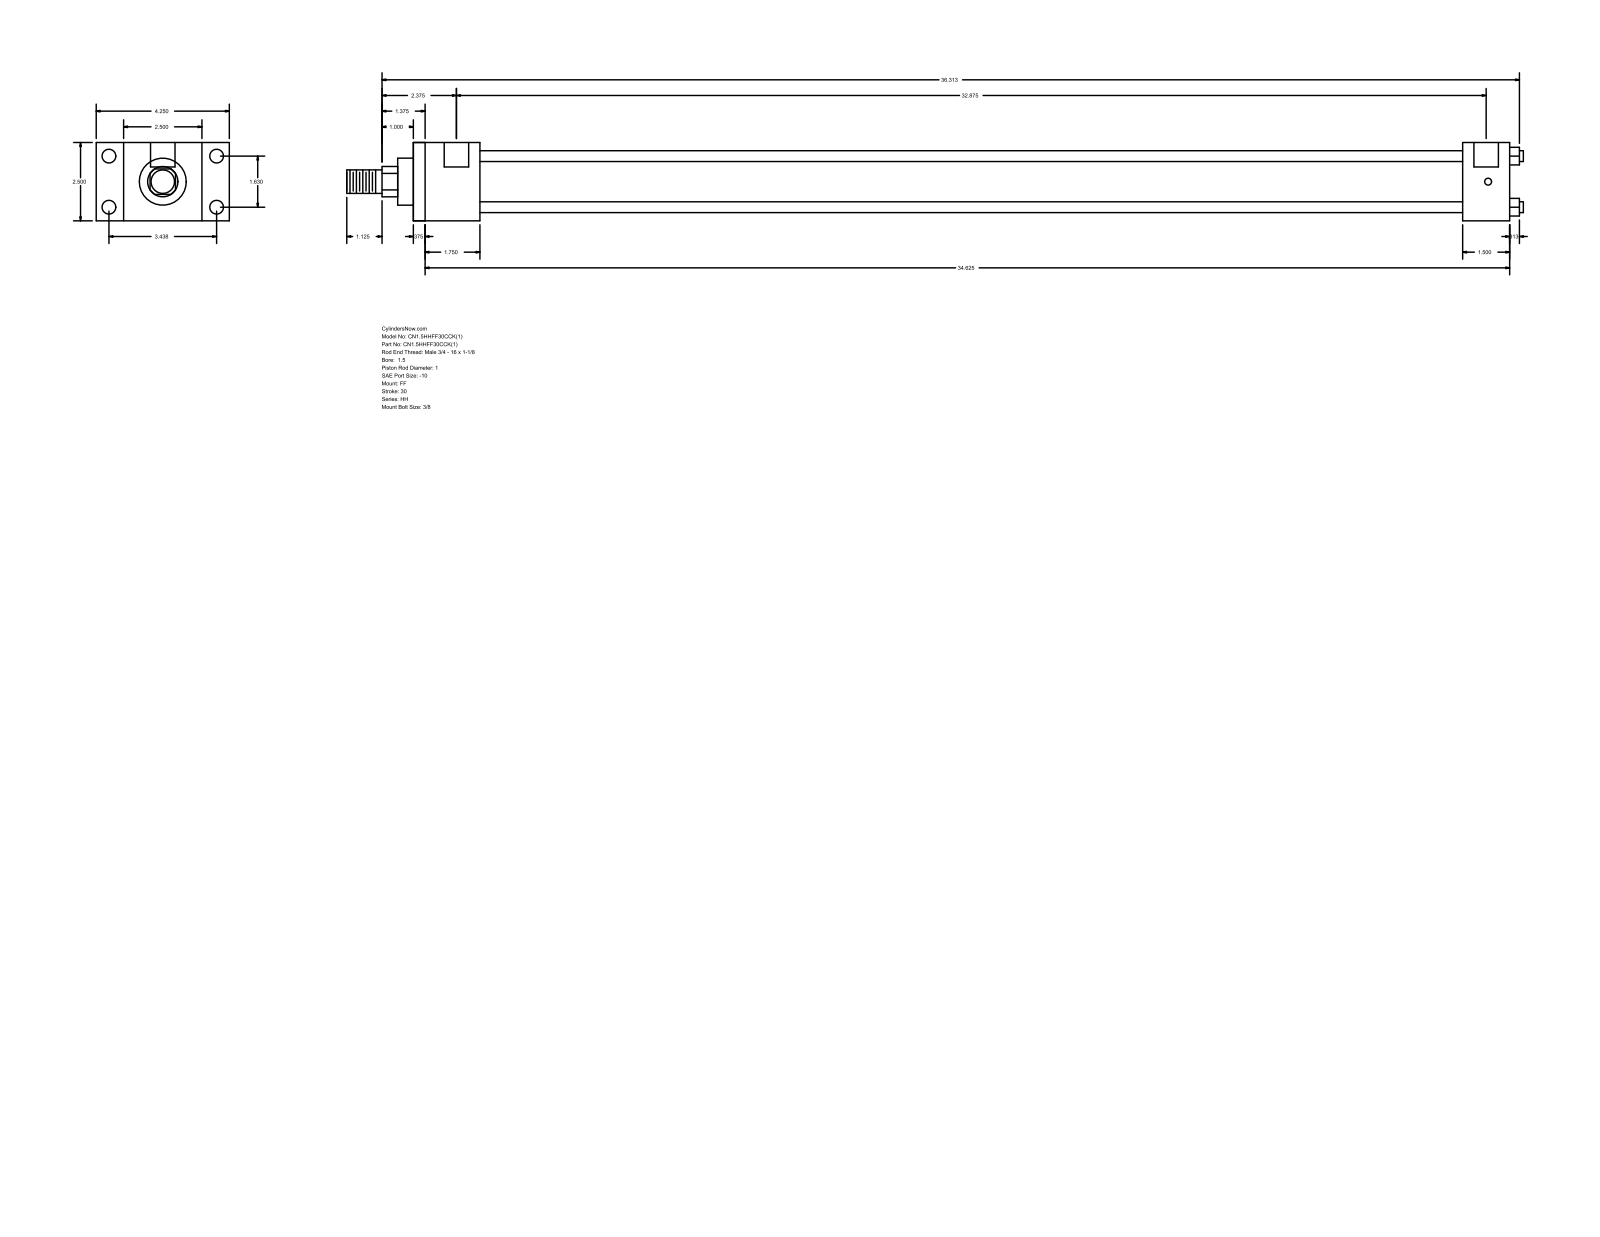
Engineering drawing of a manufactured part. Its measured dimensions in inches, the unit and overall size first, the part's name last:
Units: inches
Overall size (bounding box): 37.563 × 4.25 × 2.5
Round holes (diameter × count): ⌀0.219 ×4, ⌀0.438 ×4, ⌀0.781 ×2
Round bosses / shafts (diameter × count): ⌀0.345 ×4, ⌀1.75 ×1, ⌀1.5 ×1, ⌀1 ×1, ⌀0.75 ×1
Partial cylindrical surfaces — rounded edges, fillets, slot ends (radius × count): R0.484 ×1
Main face-to-face distances: 2.5, 35, 0.375, 34.625, 1.5, 2.125, 1.75, 32.875, 33.5, 33.125
Hole centre spacings: 0.063, 1.63, 3.438, 3.805, 32.937, 33, 32.875
Bodies: 0 solids, 92 faces (64 planar, 28 cylindrical, 0 other)
Part name (STEP PRODUCT): HH_FF__0150_1
STEP written by: GSSL Pune (CONFIG_CONTROL_DESIGN)
